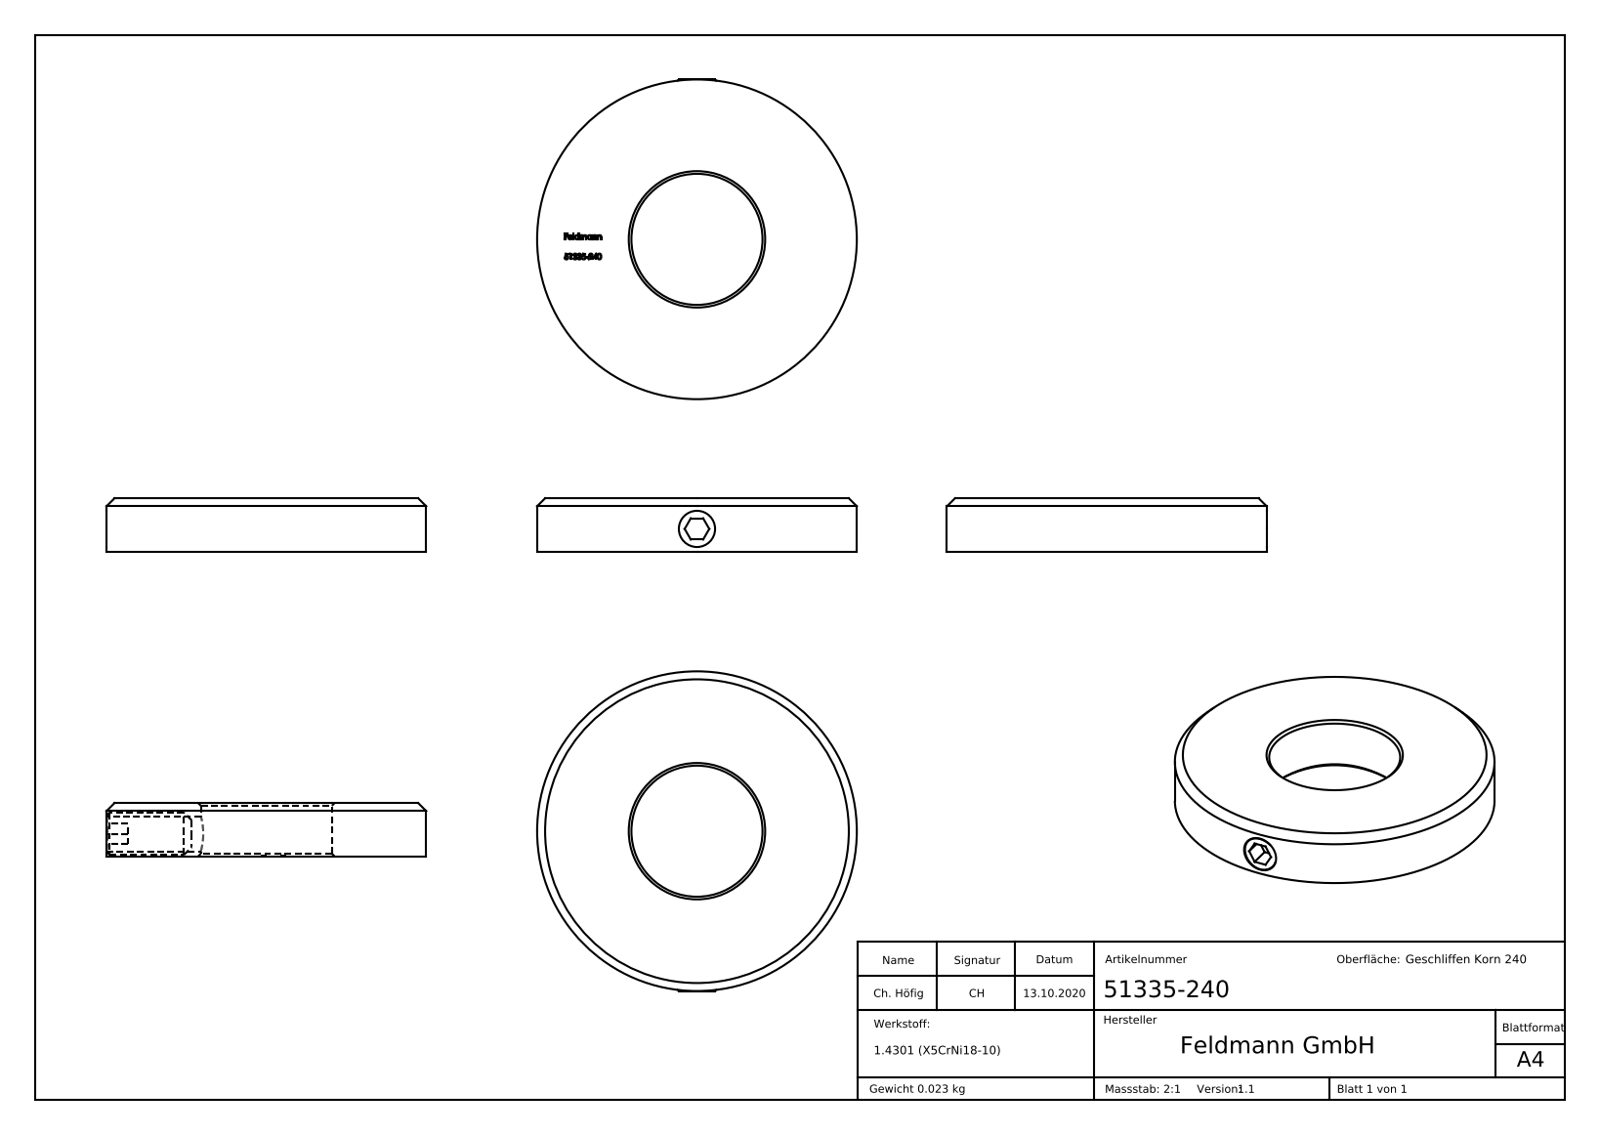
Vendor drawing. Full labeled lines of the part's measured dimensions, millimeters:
Part name (STEP PRODUCT): 51335-240; DIN913 M4x8_DIN913 M4x8; 5133X-240 Teil1_51335-240 Teil1; 5133X-240 Teil1 (+1 more)
STEP written by: SolidWorks 2018 (CONFIG_CONTROL_DESIGN)
Units: millimetres
Bodies: 2 solids, 259 faces (134 planar, 8 cylindrical, 117 other)
Overall size (bounding box): 37 × 30 × 5
Volume: 2 926 mm³ · Surface area: 1 997 mm²
Round holes (diameter × count): ⌀3.3 ×1, ⌀12.3 ×1
Round bosses / shafts (diameter × count): ⌀30 ×1, ⌀4 ×1
Main face-to-face distances: 5, 2, 8, 6, 1.88, 1.12, 3.88, 3.12, 1.02, 3.02
